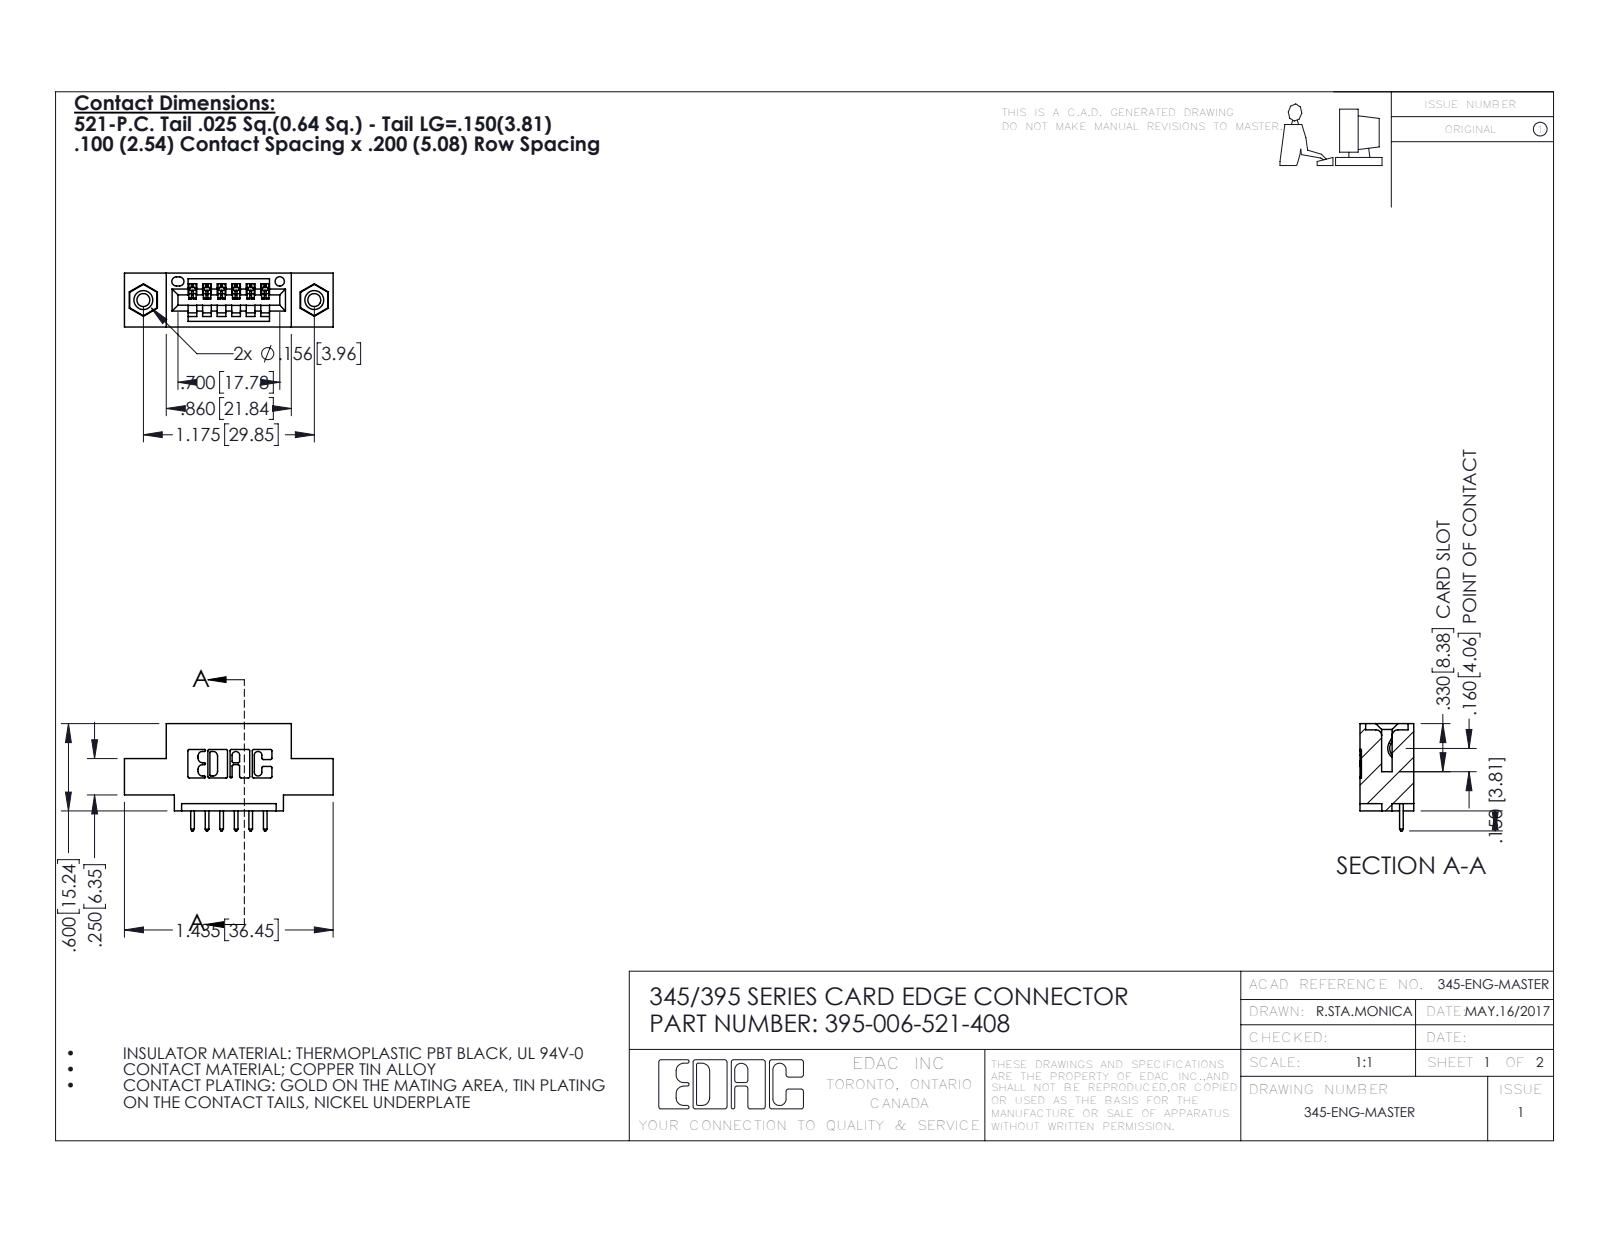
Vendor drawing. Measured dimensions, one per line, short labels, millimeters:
name: 345-292-001_345-293-121; 345 Part_0.110 Offset - 0.156 Dia-TI; 395-006-521-408; 345-250-001_345-250-003-102
written by: SolidWorks 2016 (CONFIG_CONTROL_DESIGN)
unit: mm
bodies: 9 solids, 538 faces (356 planar, 166 cylindrical, 16 other)
size: 36.4 × 18.7 × 9.4
volume: 3 060 mm³; area: 3 625 mm²
holes: 2× ⌀2.3, 2× ⌀3.2, 2× ⌀4, 1× ⌀1.6
bosses: 2× ⌀3.9
rounds: 22× R0.3, 12× R0.2, 12× R0.3, 6× R0.2, 6× R0.8, 3× R0.7, 2× R0.8, 2× R1
face distances: 5.1, 9.4, 1.8, 7.6, 2.5, 0.6, 4.1, 2.5, 6.9, 1.5
hole spacings: 6.9, 24, 29.8
